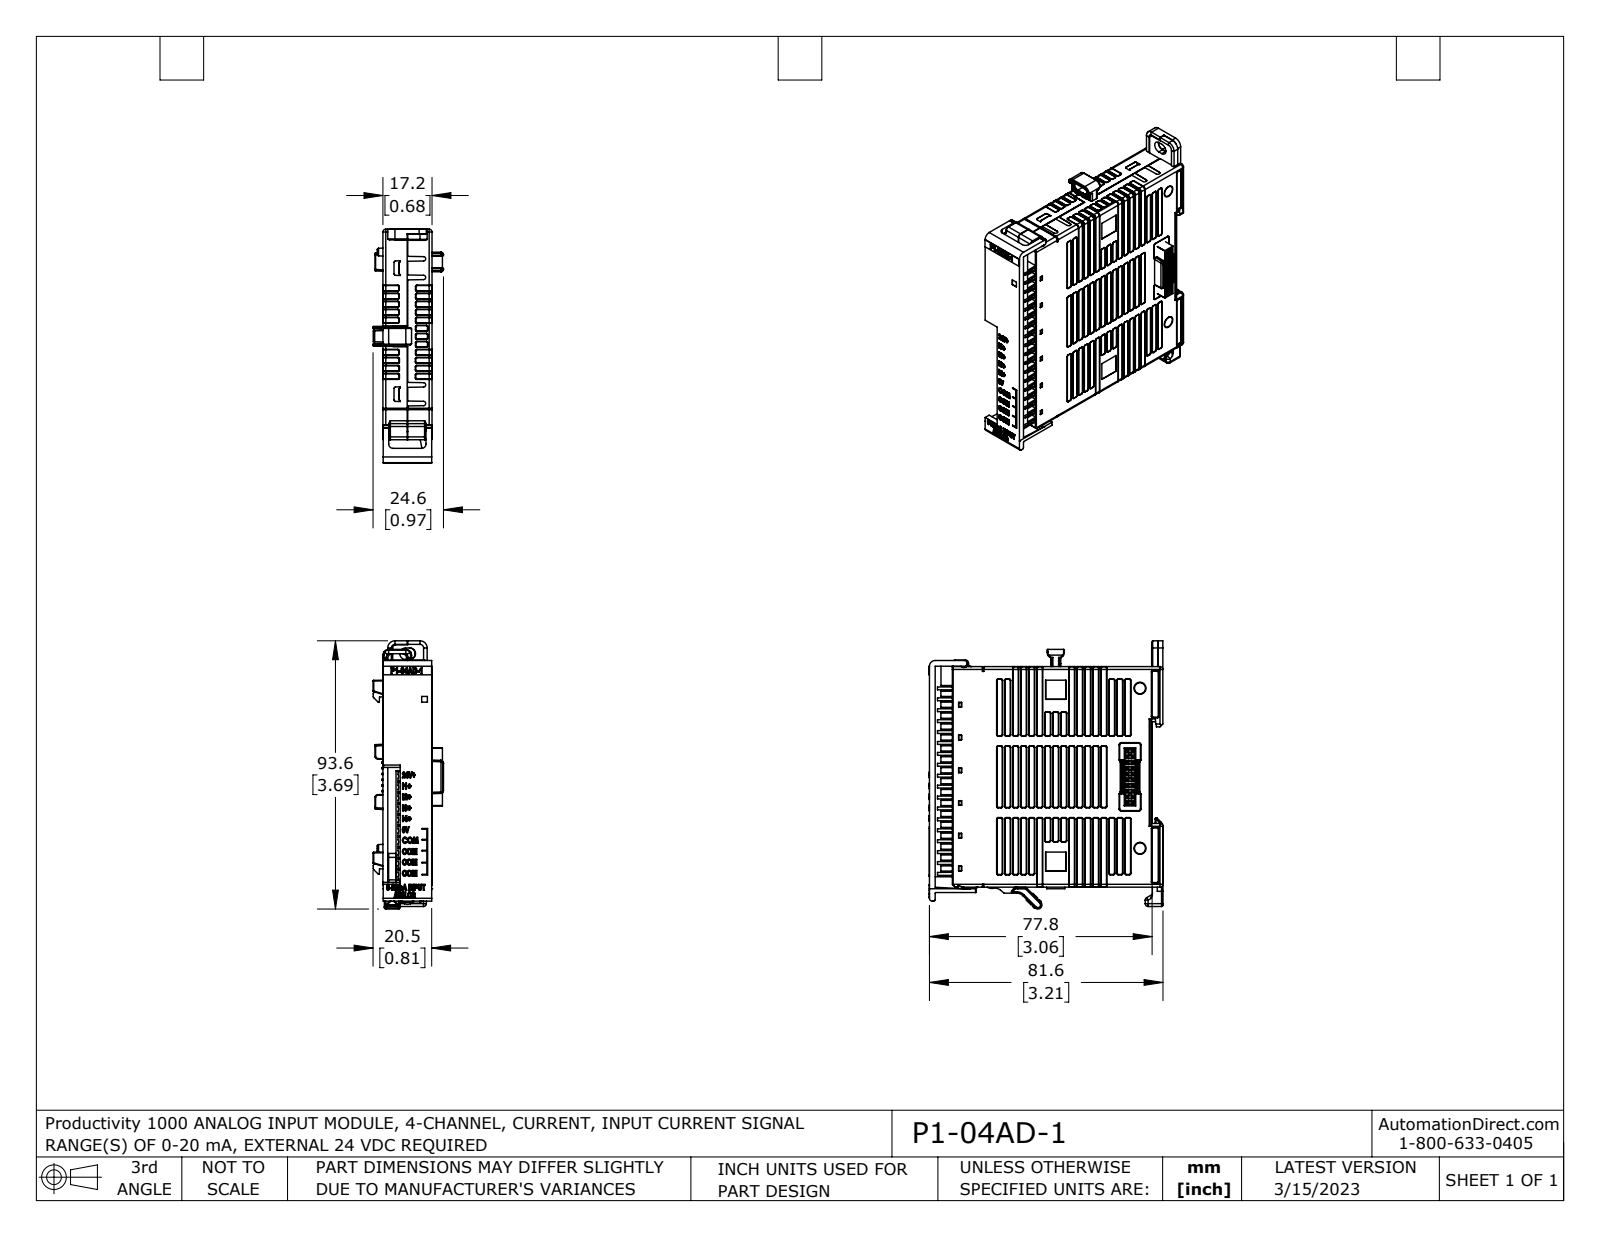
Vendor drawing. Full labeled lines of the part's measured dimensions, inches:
Part name (STEP PRODUCT): P1-04AD-1 DIN Coord fxt
STEP written by: SolidWorks 2021 (AUTOMOTIVE_DESIGN)
Units: inches
Bodies: 5 solids, 4771 faces (2603 planar, 1040 cylindrical, 1128 other)
Overall size (bounding box): 3.686 × 3.218 × 1.033
Volume: 5.59 in³ · Surface area: 47.54 in²
Round holes (diameter × count): ⌀0.01 ×20, ⌀0.024 ×8, ⌀0.049 ×1
Round bosses / shafts (diameter × count): ⌀0.043 ×2, ⌀0.064 ×1
Partial cylindrical surfaces — rounded edges, fillets, slot ends (radius × count): R0.01 ×213, R0.02 ×123, R0.039 ×64, R0.079 ×12, R0.059 ×10, R0.008 ×8, R0.03 ×8, R0.03 ×7
Main face-to-face distances: 0.674, 0.675, 0.079, 0.672, 0.315, 2.746, 3.061, 0.236, 0.071, 0.157
Hole centre spacings: 0.079, 0.157, 0.176, 0.236, 0.315, 0.394, 0.402, 0.111
